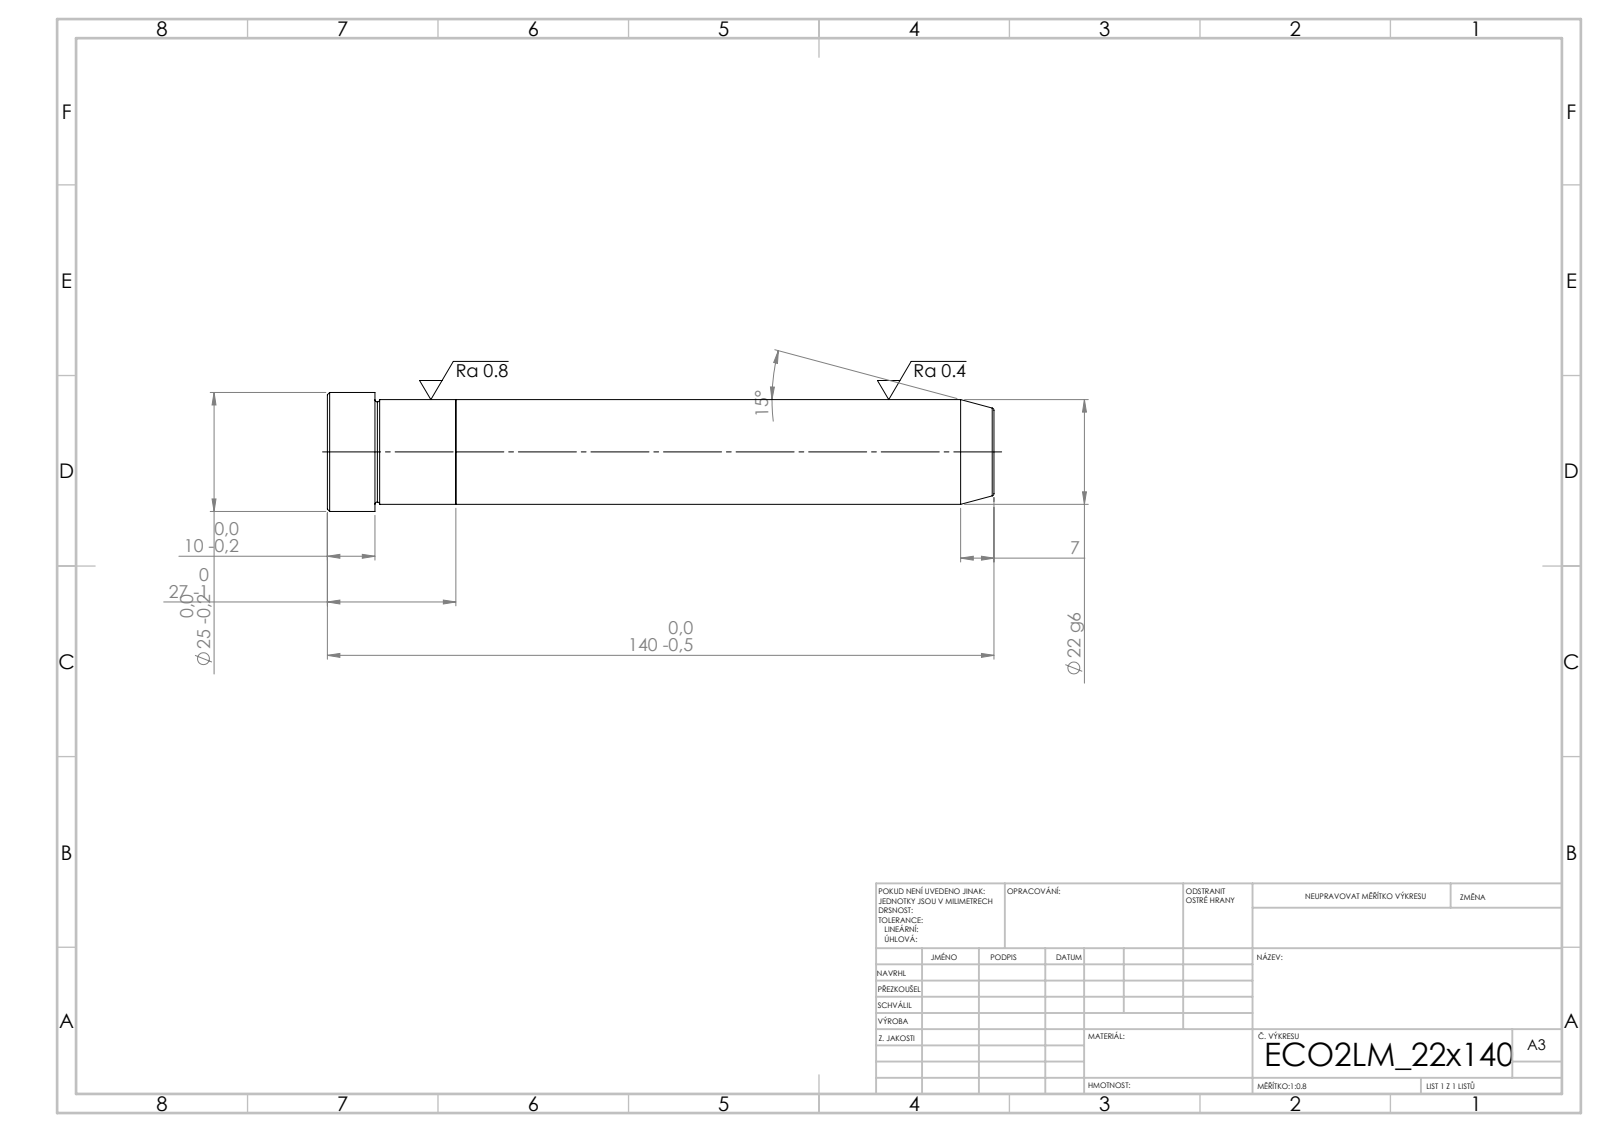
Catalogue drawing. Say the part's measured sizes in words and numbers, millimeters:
Its 3-D file was written by "SolidWorks 2019 (CONFIG_CONTROL_DESIGN)". It is 2 solids with 21 faces: 5 planar, 6 cylindrical and 10 other. Overall it measures 140 by 25 by 25 millimeters. Its volume is 53 860 cubic millimeters and its surface area 11 375 square millimeters. Round bosses or shafts: 1 of diameter 25, 1 of diameter 22. The main face-to-face distances are 27, 113, 140, 130, 17, 10.
